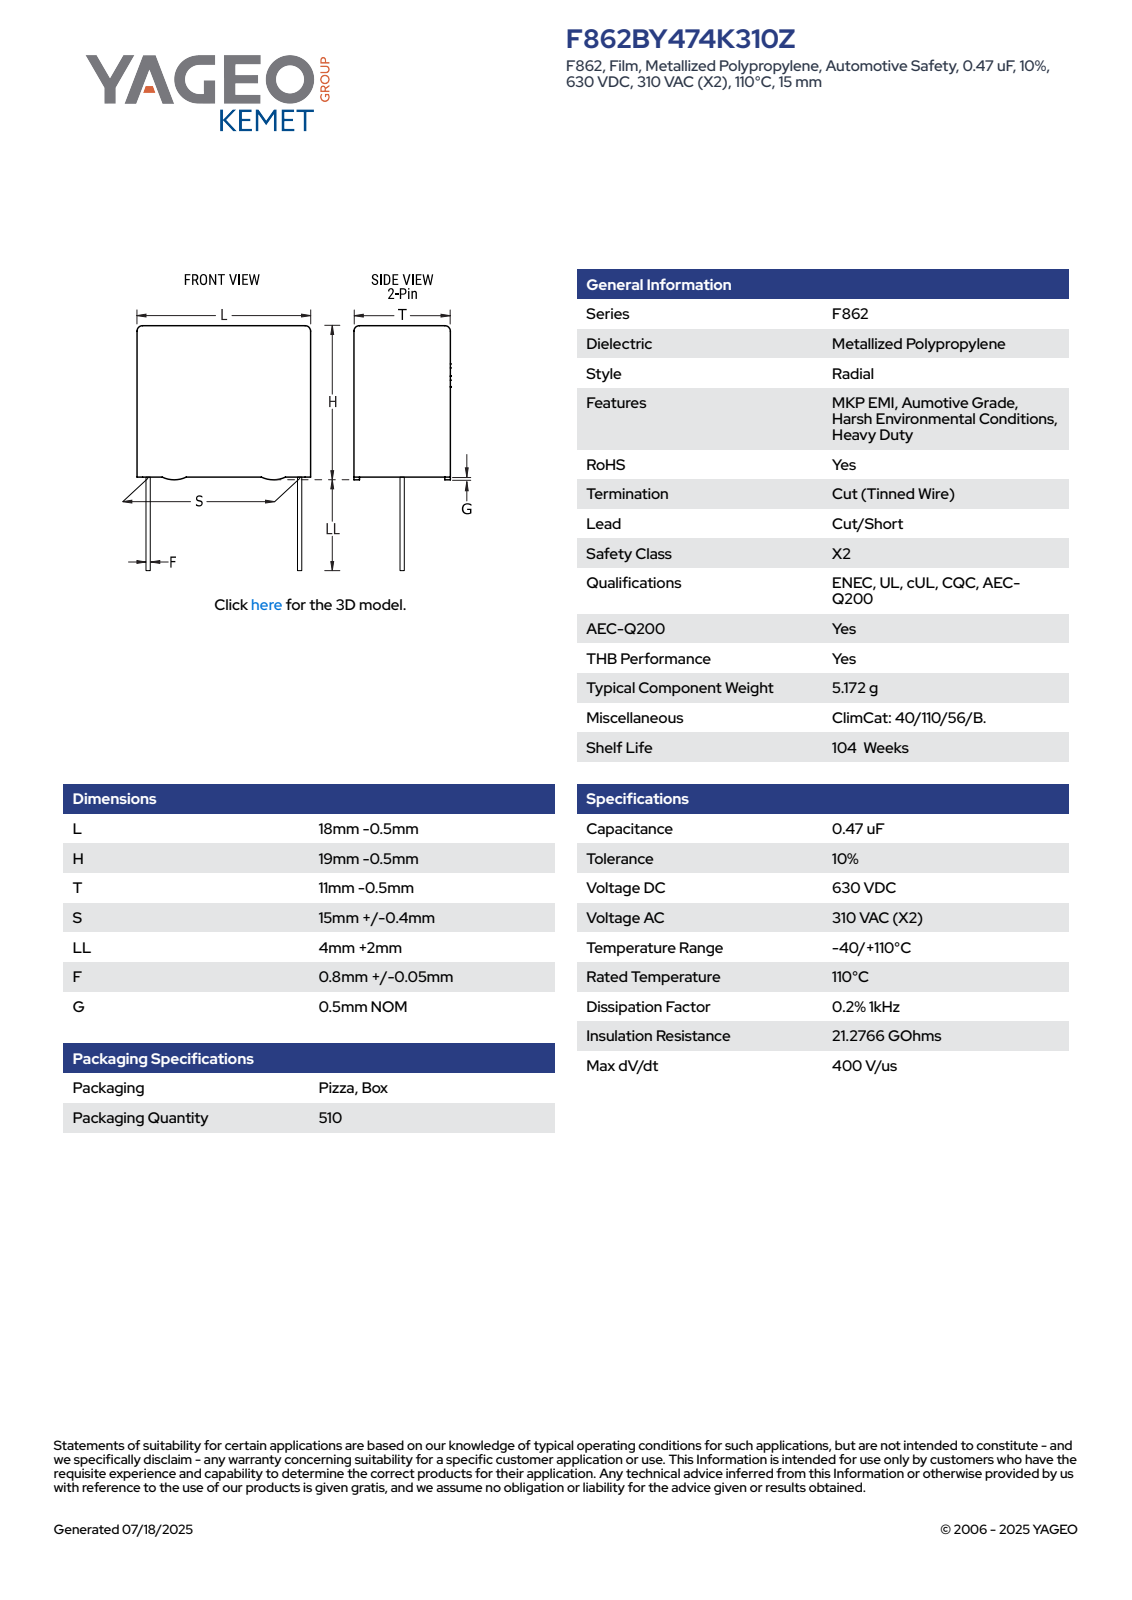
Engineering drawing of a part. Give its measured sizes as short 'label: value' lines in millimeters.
name: CFR_RBG_18X19X11_L17.5H18.5T10.5S15LL6F0.85G0.5
written by: SolidWorks 2014 (AUTOMOTIVE_DESIGN)
unit: mm
bodies: 4 solids, 89 faces (81 planar, 8 cylindrical, 0 other)
size: 24.5 × 17.5 × 10.51
volume: 3 315 mm³; area: 1 444 mm²
bosses: 2× ⌀0.85
rounds: 4× R0.5
face distances: 10.5, 17.5, 18, 10.51, 0.5, 18.5, 0.6, 9.9, 0.61, 9.3
